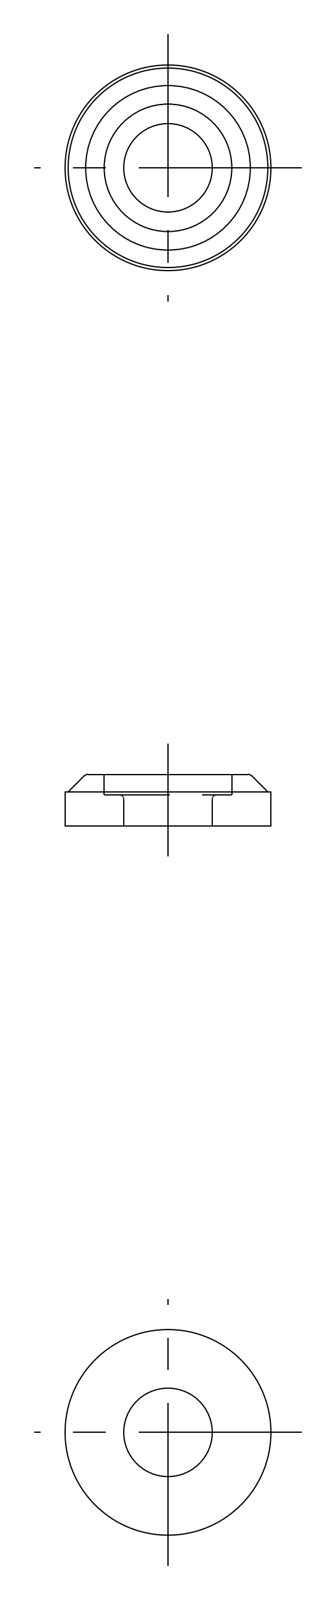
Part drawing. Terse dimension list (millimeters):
name: facing ring; THA_270_2
written by: SolidWorks 2015 (AUTOMOTIVE_DESIGN)
unit: mm
bodies: 1 solid, 16 faces (4 planar, 6 cylindrical, 6 other)
size: 10 × 10 × 2.5
volume: 130 mm³; area: 228 mm²
holes: 1× ⌀4.3, 1× ⌀6.2
bosses: 1× ⌀10
face distances: 2.5, 1.5, 1, 1.65, 0.85
